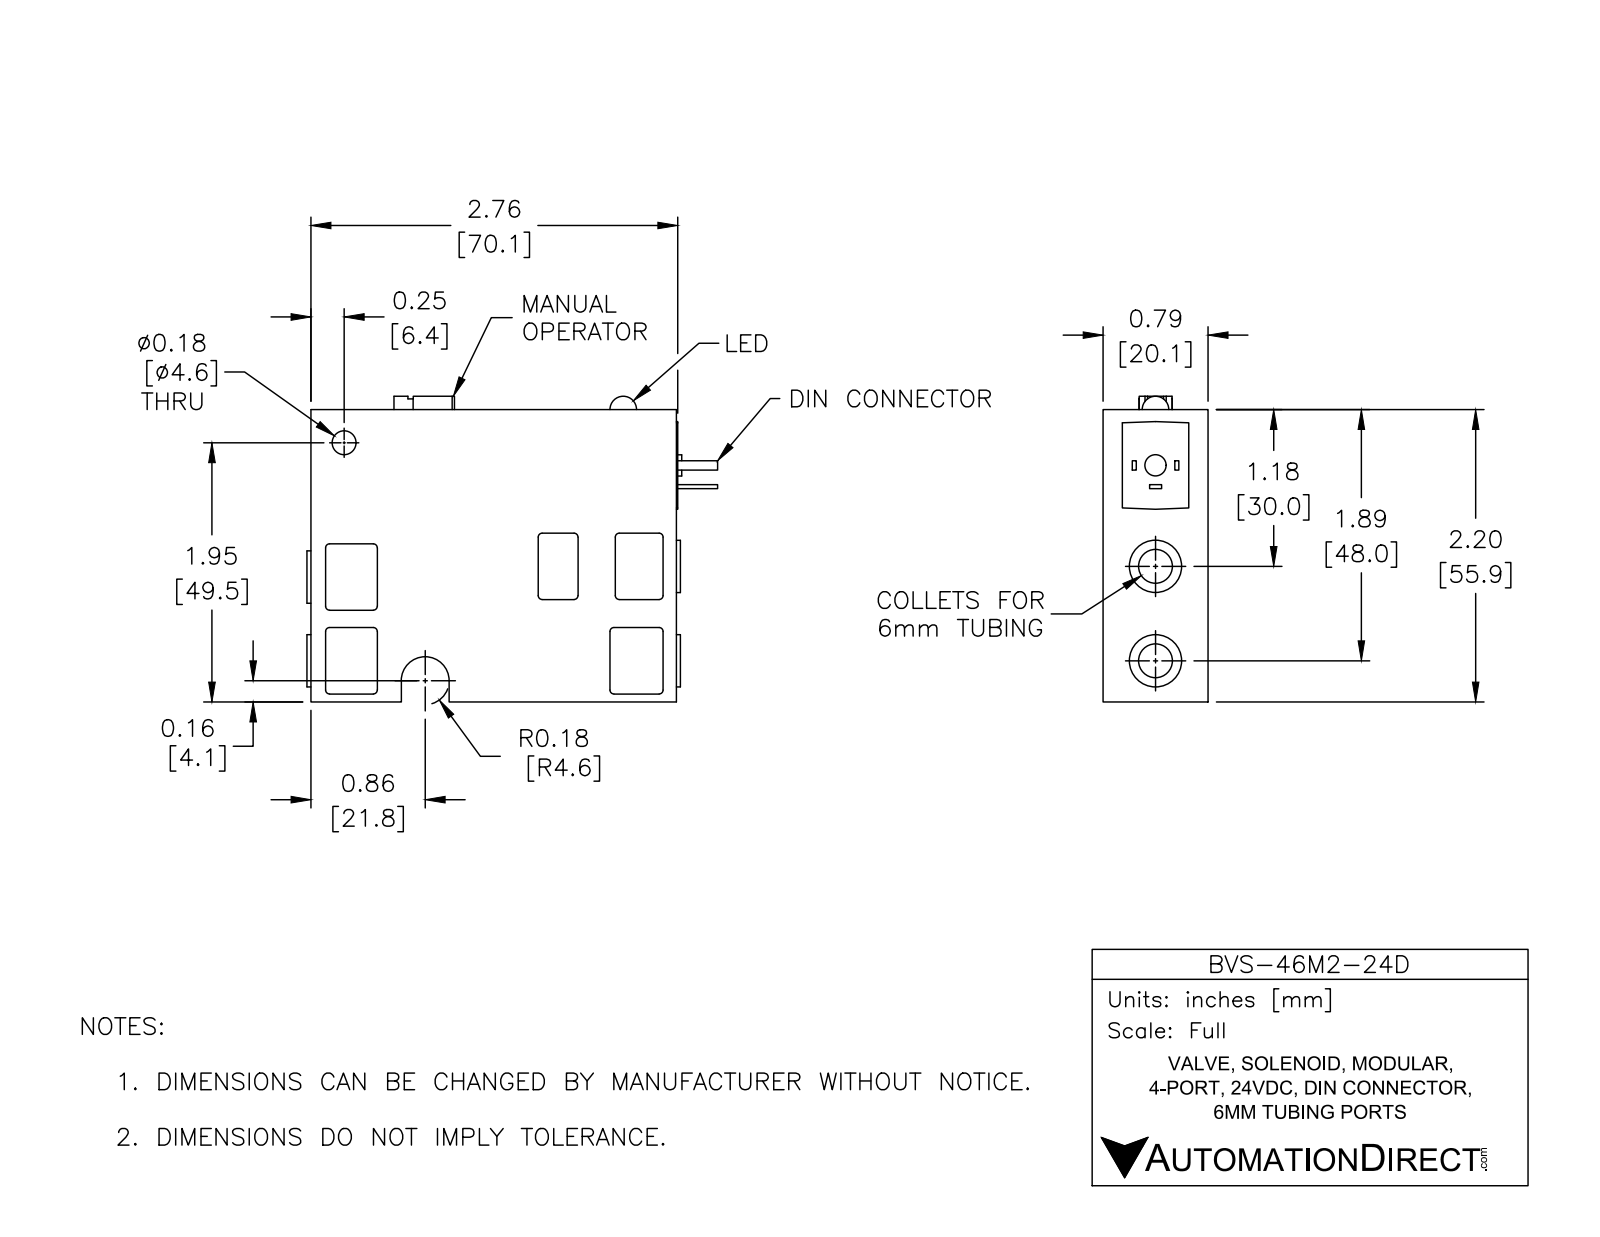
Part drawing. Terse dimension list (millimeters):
name: BVS-46M2-24D
written by: SolidWorks 2016 (AUTOMOTIVE_DESIGN)
unit: mm
bodies: 1 solid, 169 faces (99 planar, 68 cylindrical, 2 other)
size: 78.5 × 58.4 × 20.1
volume: 71 680 mm³; area: 16 250 mm²
holes: 3× ⌀6.5, 1× ⌀2.5, 1× ⌀4.6
bosses: 3× ⌀10, 1× ⌀4.1
rounds: 20× R0.8, 2× R0.5, 1× R3.2, 1× R4.6
face distances: 20.1, 2.5, 55.9, 17.5, 69.9, 15, 12.7, 2.8, 67.3, 0.8
hole spacings: 2, 14, 16, 16, 18, 32
